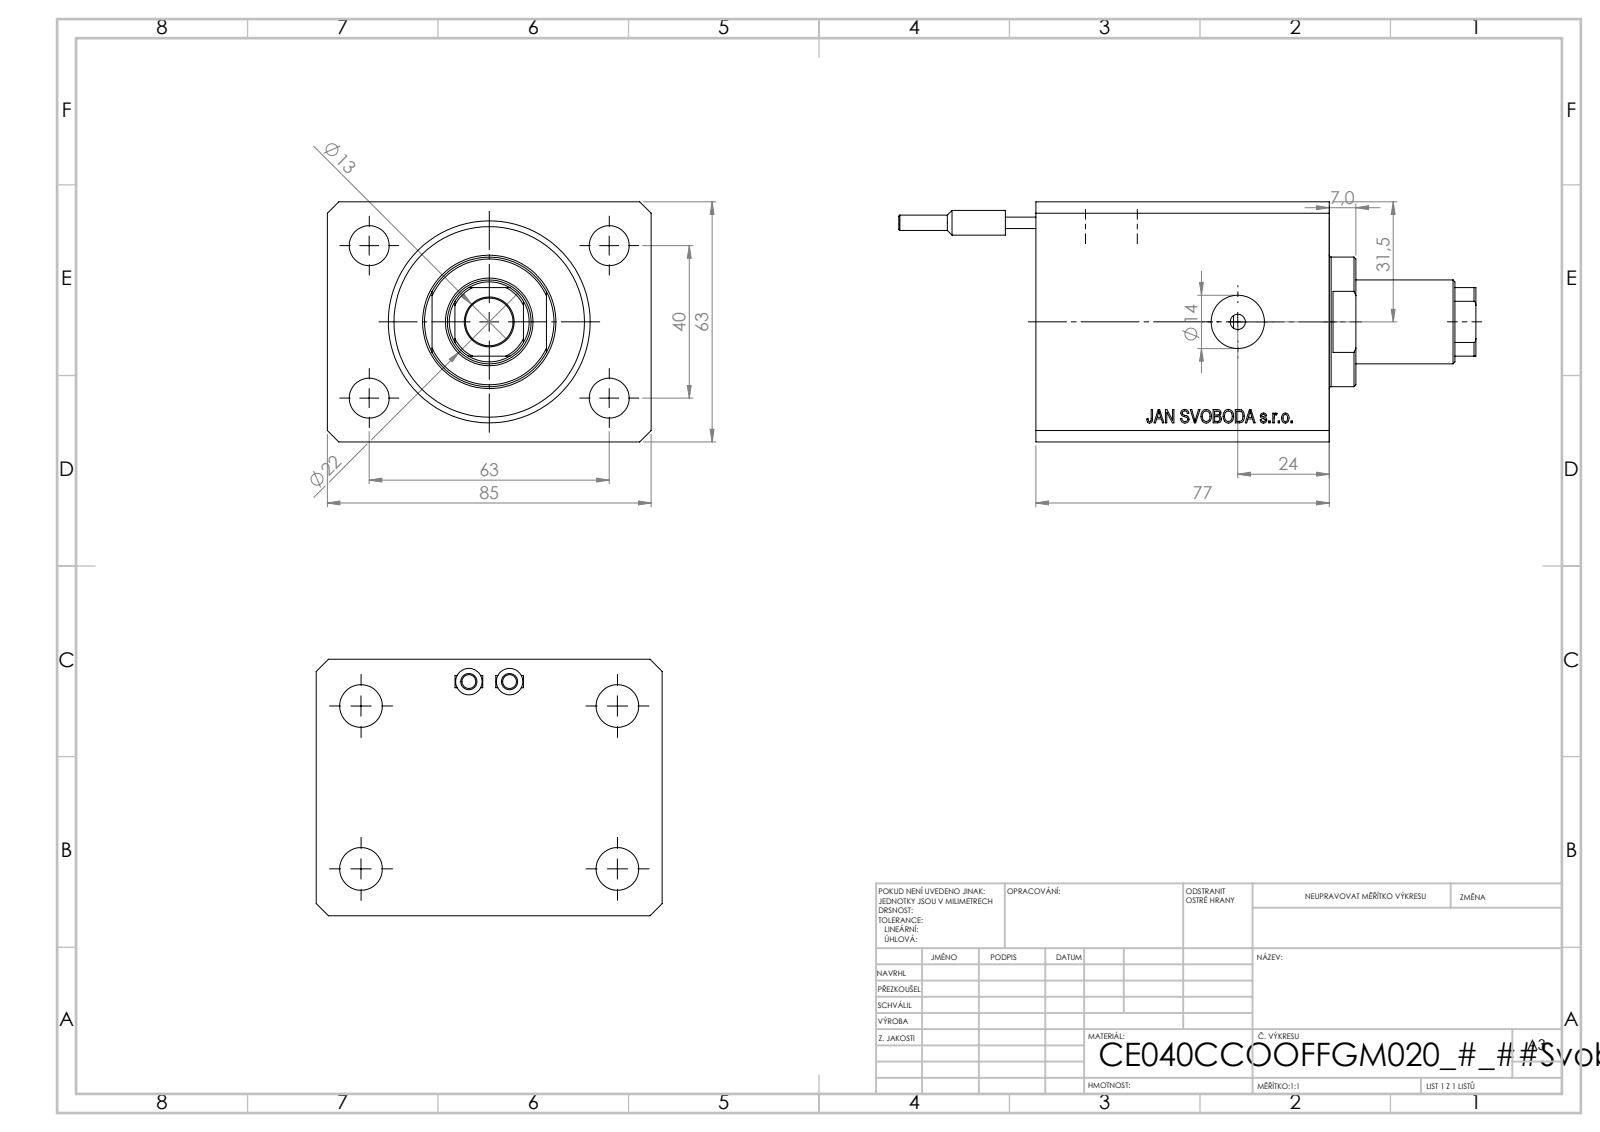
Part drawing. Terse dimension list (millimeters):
name: SWITCH_V250CE; V250CE_C_Body; V250CE_VC_C; V250CE_C_VCP
written by: SolidWorks 2019 (CONFIG_CONTROL_DESIGN)
unit: mm
bodies: 5 solids, 905 faces (457 planar, 48 cylindrical, 400 other)
size: 151.5 × 85 × 63
volume: 404 443 mm³; area: 74 859 mm²
holes: 4× ⌀10.5, 2× ⌀4, 2× ⌀14, 1× ⌀12.5, 1× ⌀22, 1× ⌀40, 1× ⌀53
bosses: 2× ⌀6.8, 2× ⌀6.5, 2× ⌀4, 1× ⌀34
rounds: 1× R10.5
face distances: 63, 85, 77, 51.9, 25.1, 32, 45, 19.9, 20, 57
hole spacings: 37.31, 40, 63, 74.63, 29
